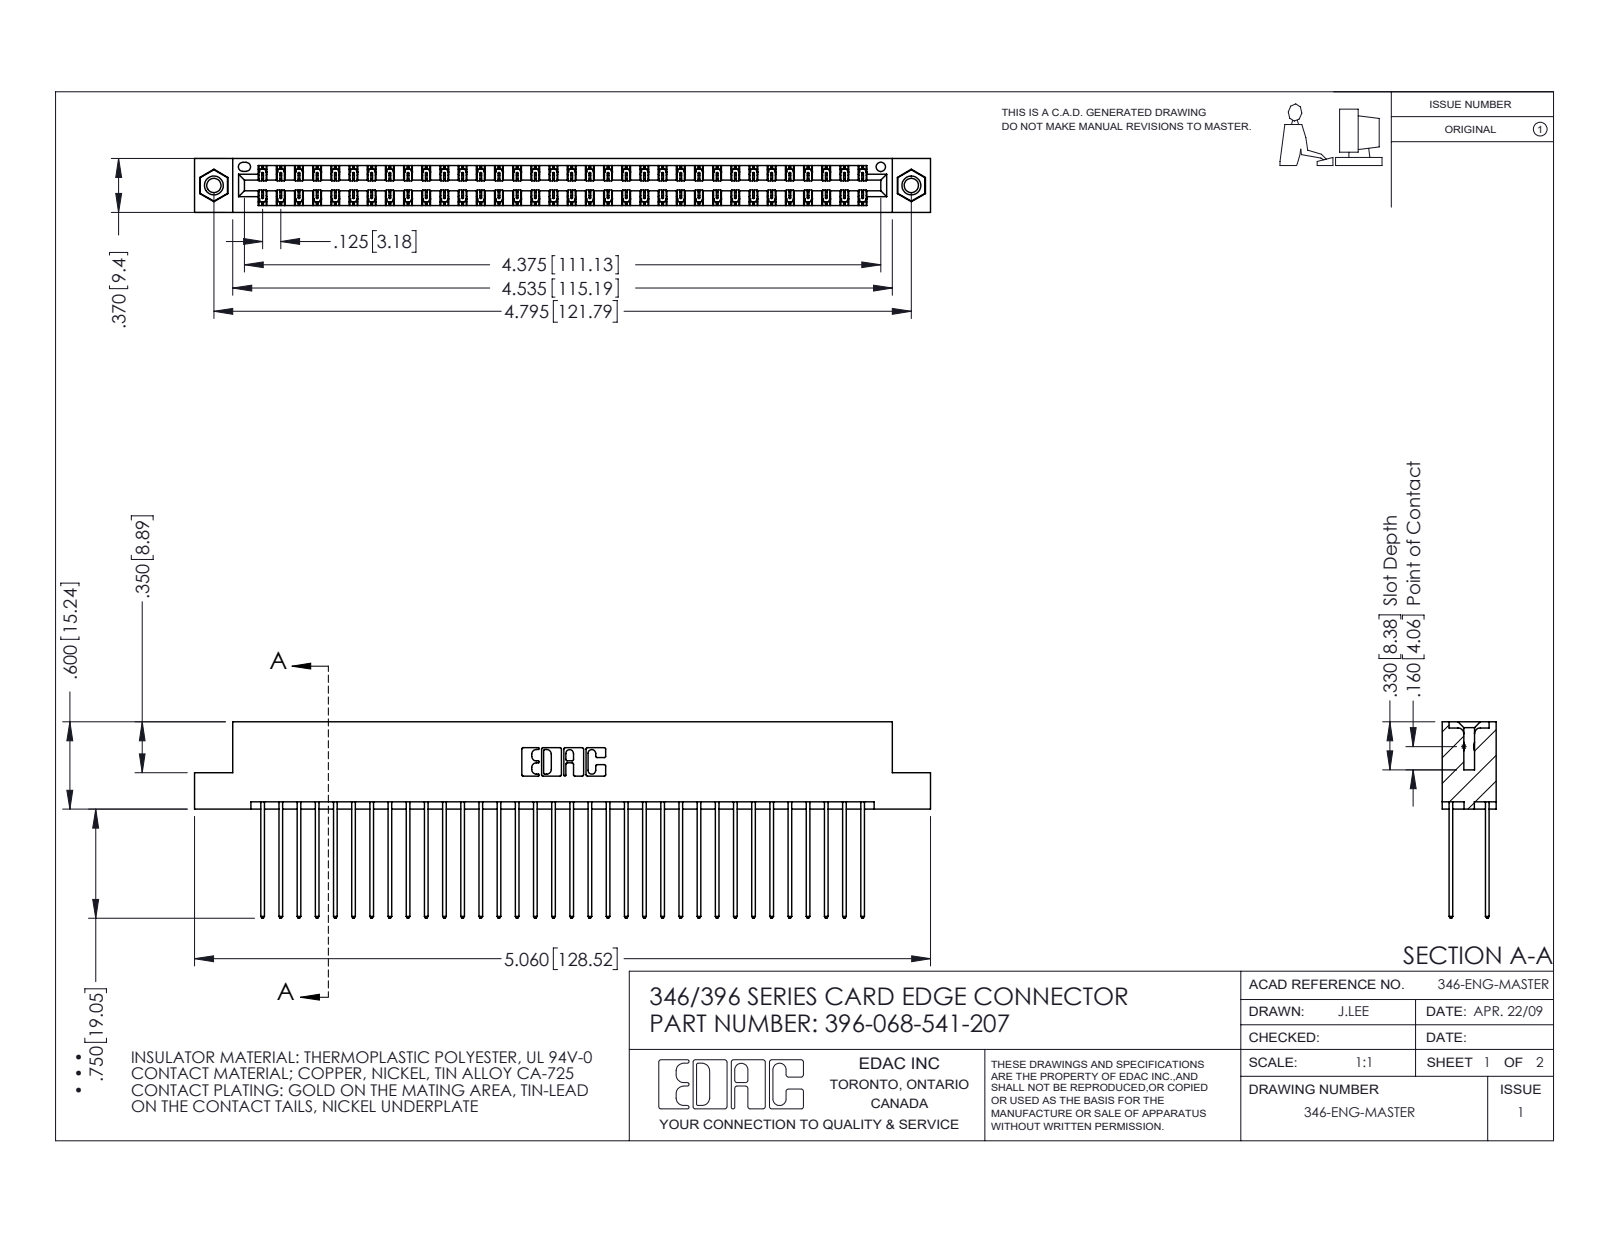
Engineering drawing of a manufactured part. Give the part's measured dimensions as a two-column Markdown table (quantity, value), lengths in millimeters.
| quantity | value |
| --- | --- |
| part name | 346 Part_Flush Mounting Lugs - 0.156 Dia-TI; 345-292-001_345-293-141; 396-068-541-207; 345-250-001_345-250-005-103 |
| STEP written by | SolidWorks 2016 (CONFIG_CONTROL_DESIGN) |
| units | millimeters |
| bodies | 71 solids, 3718 faces (2488 planar, 1214 cylindrical, 16 other) |
| overall size | 128.5 × 34.3 × 9.4 |
| volume | 12 800 mm³ |
| surface area | 19 440 mm² |
| round holes (diameter × count) | 2.5 × 2, 3.2 × 2, 4 × 2, 1.6 × 1 |
| round bosses / shafts (diameter × count) | 3.9 × 2 |
| partial cylindrical surfaces (radius × count) | 0.2 × 102, 0.3 × 68, 0.3 × 22, 0.2 × 6, 0.8 × 6, 0.7 × 3, 0.4 × 2, 0.6 × 2 |
| main face-to-face distances | 1.2, 8.2, 6.4, 1.8, 7.6, 0.6, 9.4, 7, 5.7, 3.8 |
| hole center spacings | 6.2, 116.5, 121.8 |
